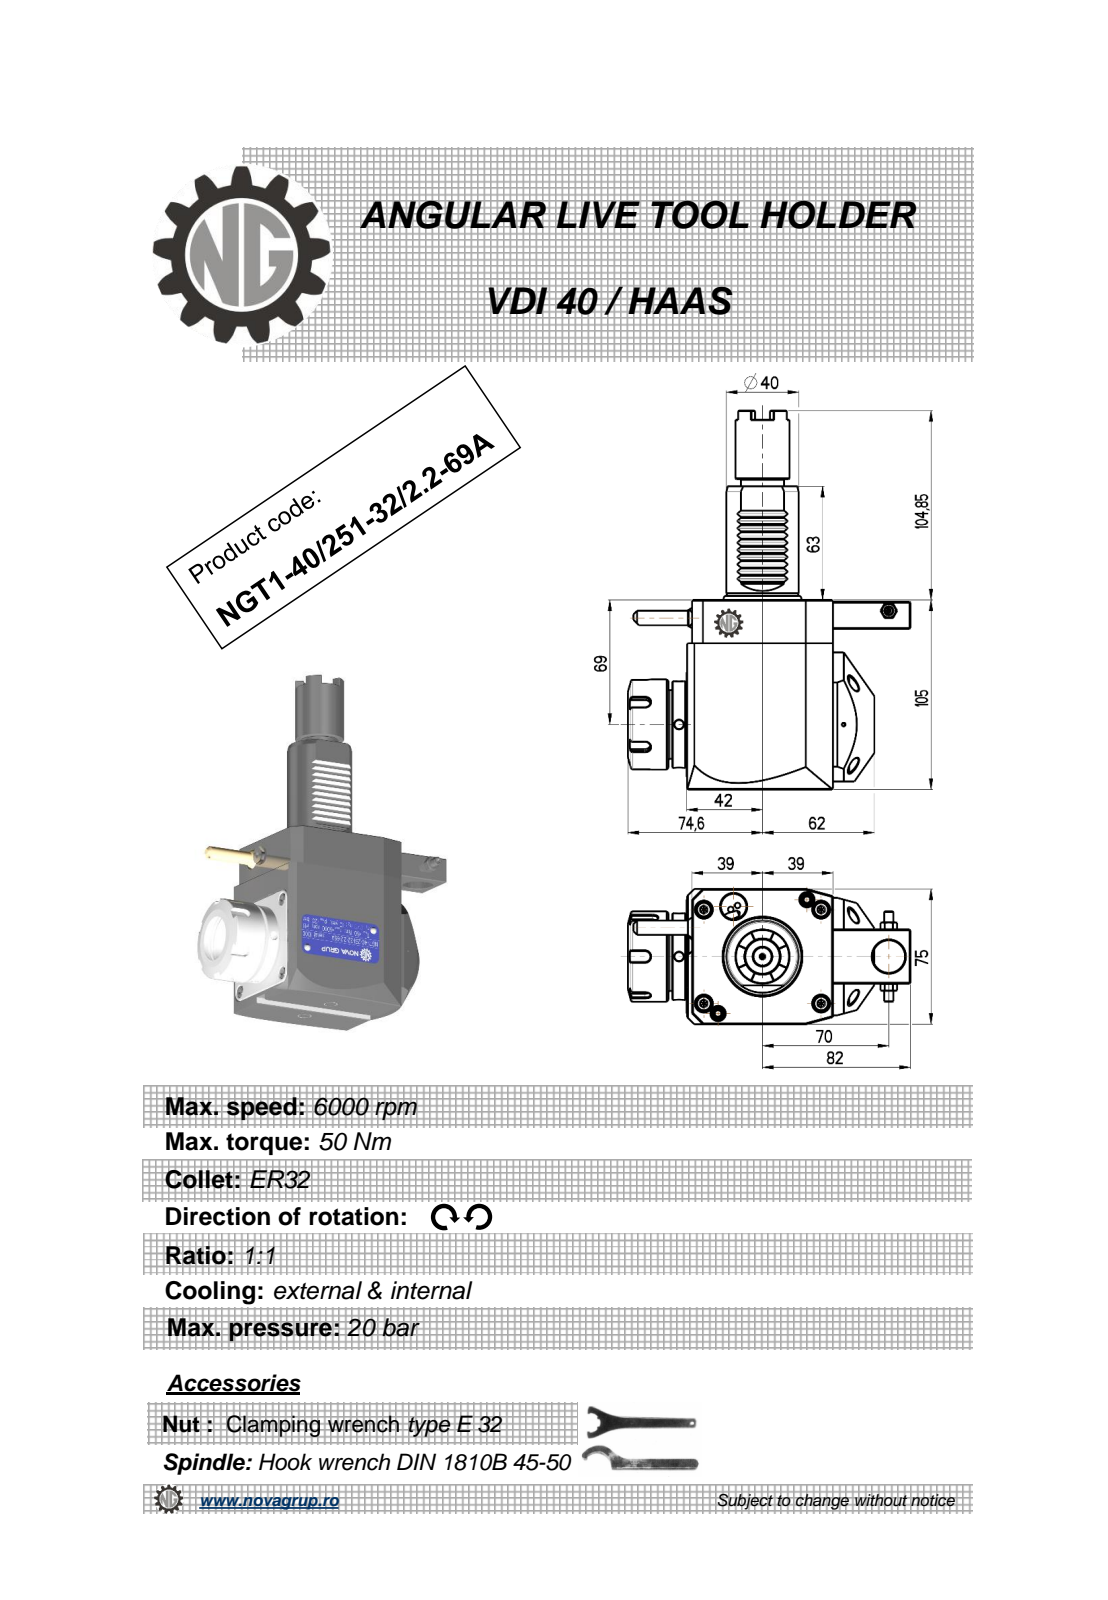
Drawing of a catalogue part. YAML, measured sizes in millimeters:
part_name: "NGT1_40_251_32_2_2_69A"
step_written_by: "PRO/ENGINEER BY PARAMETRIC TECHNOLOGY CORPORATION, 2010280 (CONFIG_CONTROL_DESIGN)"
units: millimeters
bodies: {solids: 1, faces: 453, planar: 222, cylindrical: 94, other: 137}
overall_size: [209.85, 156.6, 76.6]
volume: 858987
surface_area: 73167
round_holes:
  - {diameter: 5, count: 3}
  - {diameter: 3, count: 1}
  - {diameter: 4.2, count: 1}
  - {diameter: 9.5, count: 1}
  - {diameter: 18, count: 1}
  - {diameter: 27, count: 1}
round_bosses_or_shafts:
  - {diameter: 50, count: 1}
  - {diameter: 48, count: 1}
  - {diameter: 41, count: 1}
  - {diameter: 40, count: 1}
  - {diameter: 30, count: 1}
  - {diameter: 24, count: 1}
  - {diameter: 10, count: 1}
  - {diameter: 8.96, count: 1}
partial_cylinders:
  - {radius: 0.26, count: 12}
  - {radius: 0.3, count: 10}
  - {radius: 0.2, count: 6}
  - {radius: 3, count: 5}
  - {radius: 0.5, count: 1}
  - {radius: 9.75, count: 1}
  - {radius: 40, count: 1}
face_to_face_distances: [75, 105, 81, 104, 80.8, 1, 101, 22.5, 3, 89]
hole_center_spacings: [16.19, 61.13, 61.5, 116.25, 132.22]
